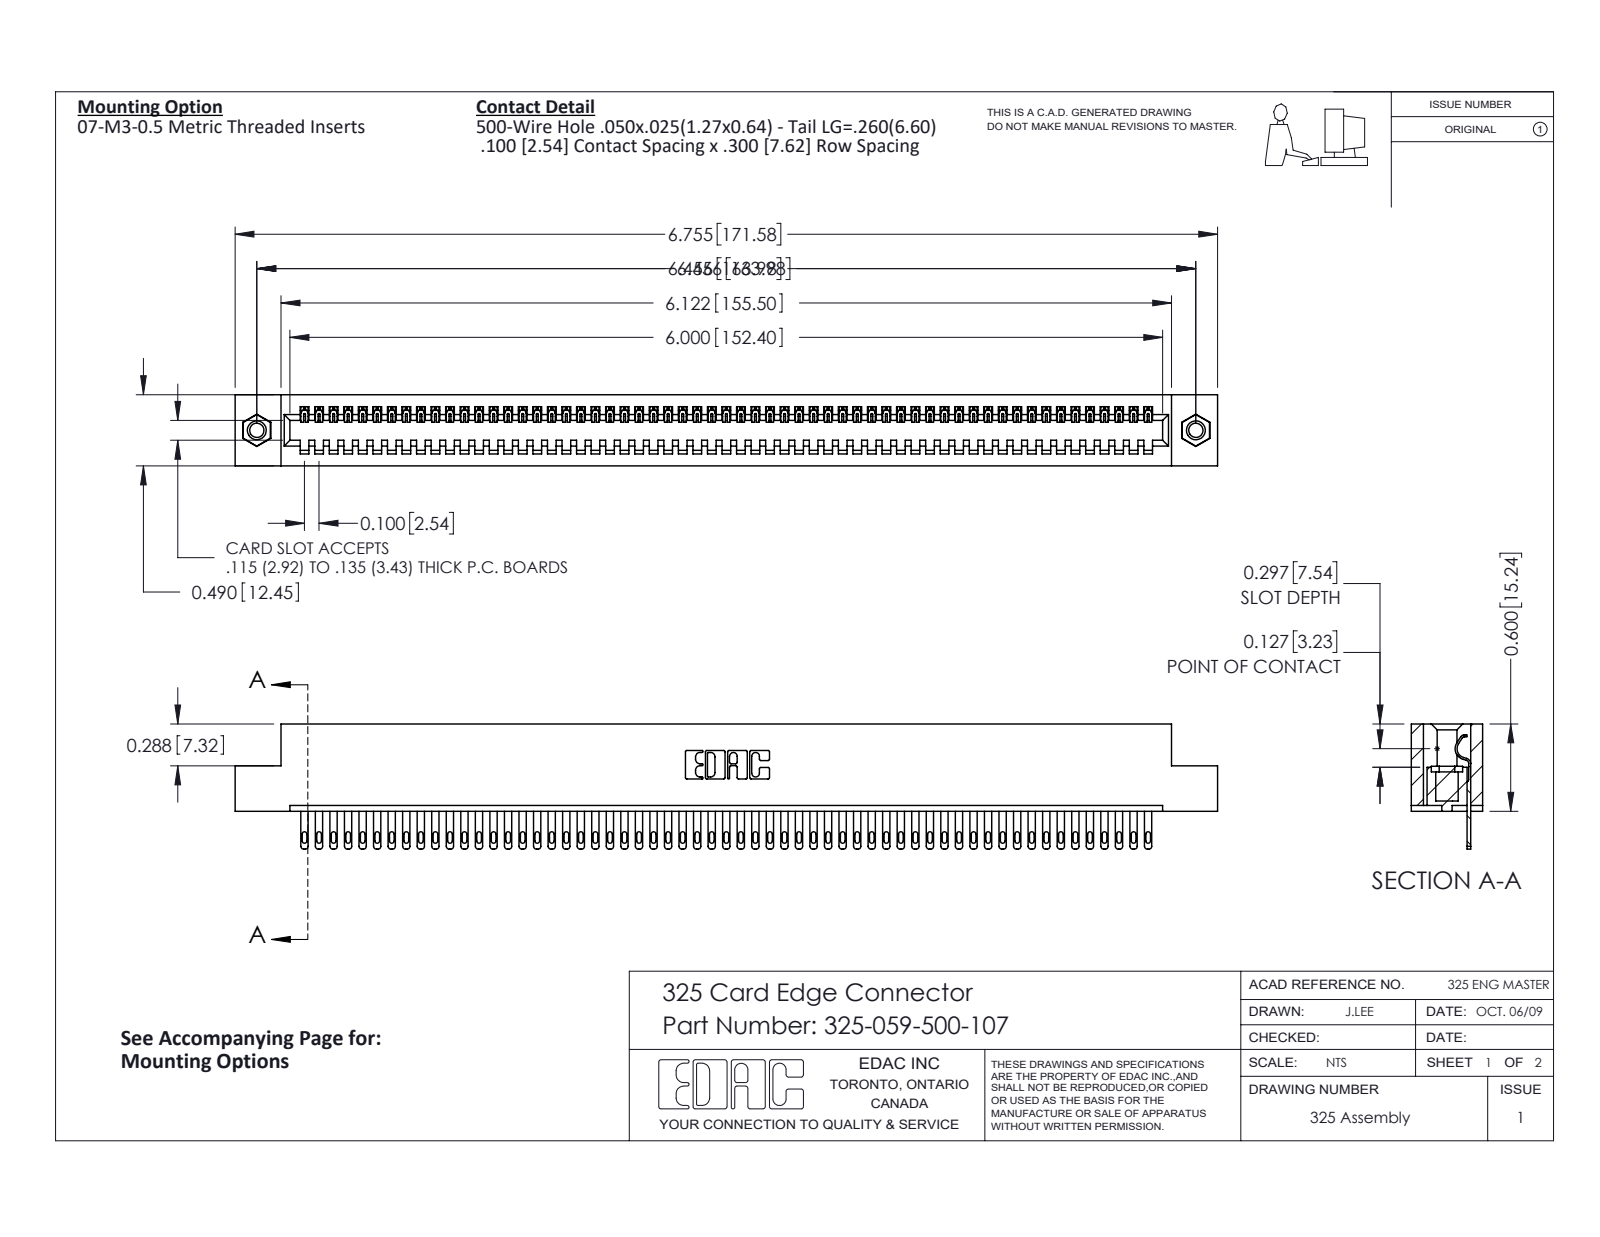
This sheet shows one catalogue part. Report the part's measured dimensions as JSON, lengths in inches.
{"part_name": "325 Part_TI; 345-250-001_345-250-005-103; 325-059-500-107; 325-292-001_325-293-100", "step_written_by": "SolidWorks 2016 (CONFIG_CONTROL_DESIGN)", "units": "inches", "bodies": {"solids": 62, "faces": 3360, "planar": 2226, "cylindrical": 1118, "other": 16}, "overall_size": [6.755, 0.86, 0.49], "volume_in3": 1.339, "surface_area_in2": 37.85, "round_holes": [[0.098, 2], [0.125, 2], [0.16, 2]], "round_bosses_or_shafts": [[0.155, 2]], "partial_cylinders_radius": [[0.006, 118], [0.016, 118], [0.02, 118], [0.01, 22], [0.007, 6], [0.031, 6], [0.026, 3], [0.014, 1]], "face_to_face_distances": [0.083, 0.407, 0.3, 0.49, 0.107, 0.383, 0.025, 0.325, 0.56, 0.263], "hole_center_spacings": [6.456]}
